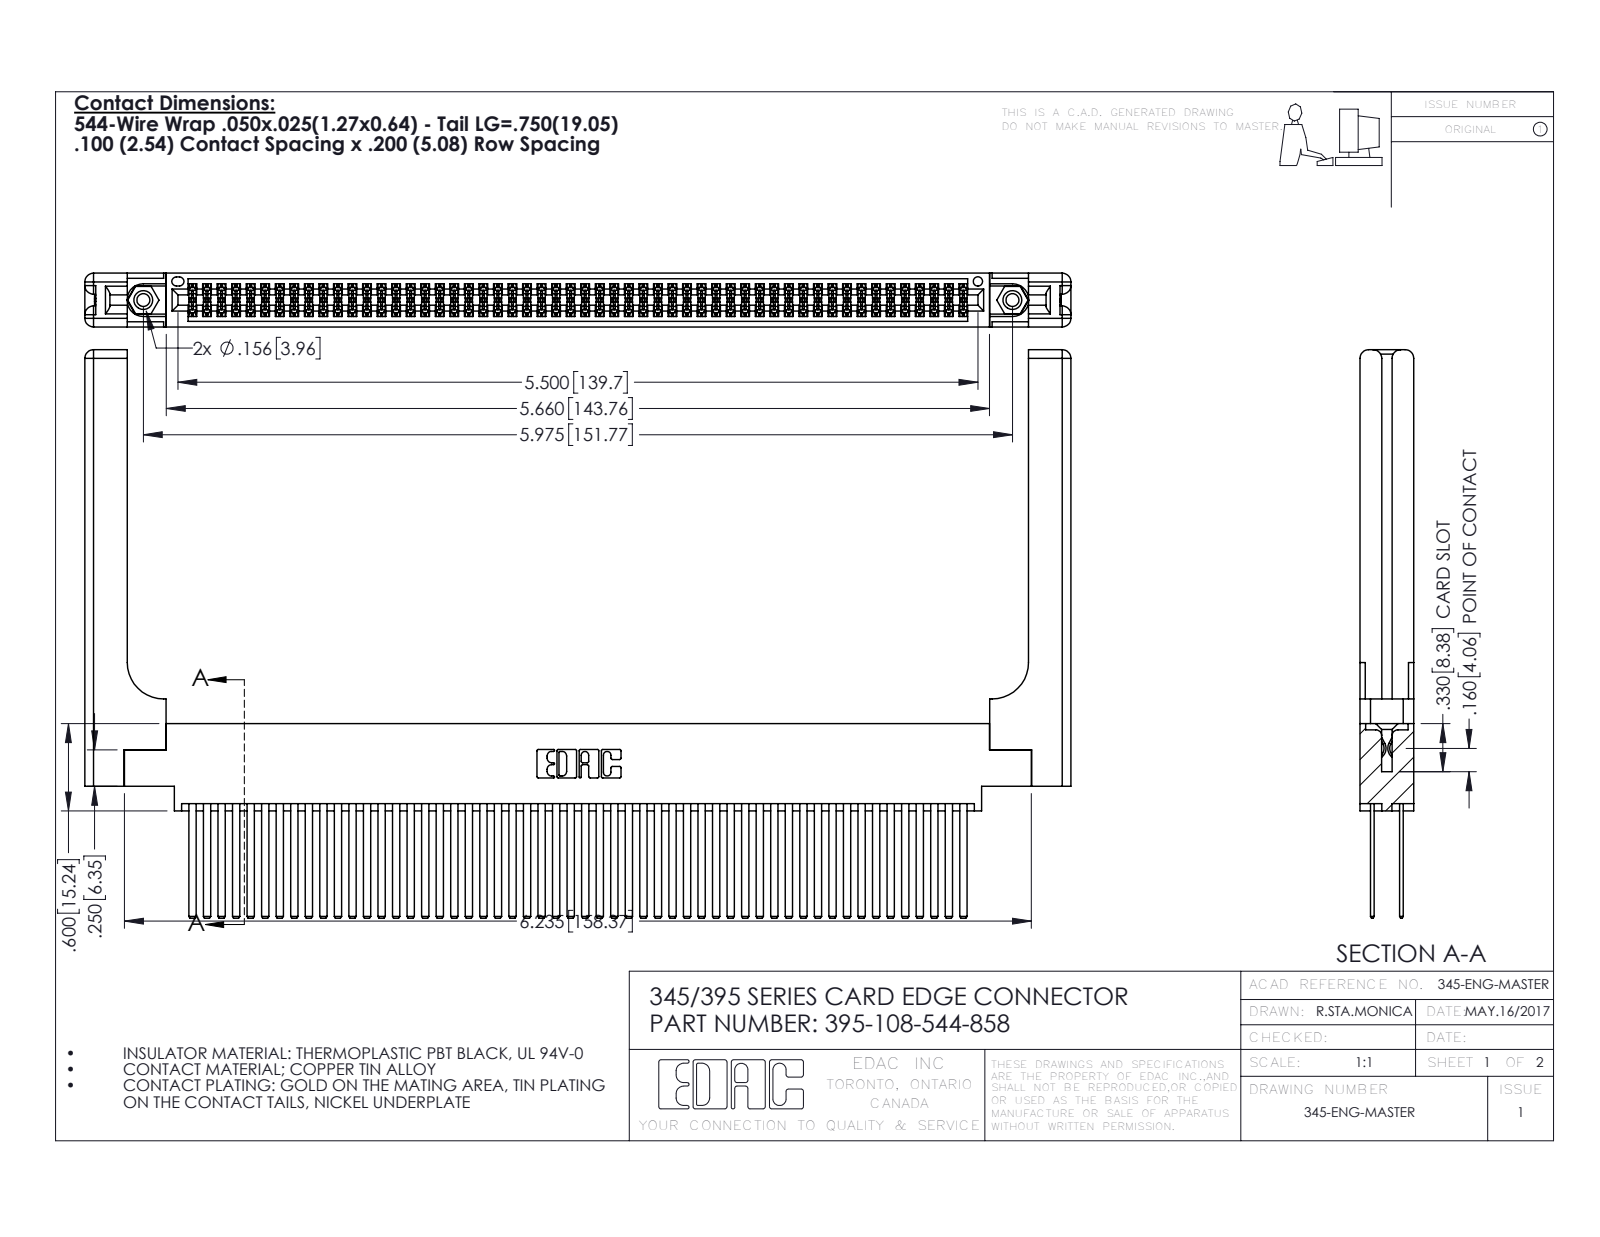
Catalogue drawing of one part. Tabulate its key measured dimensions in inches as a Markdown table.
| quantity | value |
| --- | --- |
| part name | 345 Part_0.170 Offset - 0.156 Dia-TH; 345-292-001_345-293-144; 395-108-544-858; 345-220-058_345-220-058 (+1 more) |
| STEP written by | SolidWorks 2016 (CONFIG_CONTROL_DESIGN) |
| units | inches |
| bodies | 113 solids, 5138 faces (3364 planar, 1714 cylindrical, 60 other) |
| overall size | 6.779 × 3.907 × 0.37 |
| volume | 1.63 in³ |
| surface area | 57.09 in² |
| round holes (diameter × count) | 0.089 × 2, 0.125 × 2, 0.156 × 2, 0.064 × 1 |
| round bosses / shafts (diameter × count) | 0.155 × 2 |
| partial cylindrical surfaces (radius × count) | 0.006 × 162, 0.01 × 22, 0.06 × 16, 0.007 × 6, 0.031 × 6, 0.026 × 3, 0.014 × 2, 0.019 × 2 |
| main face-to-face distances | 0.072, 0.298, 0.098, 0.272, 0.025, 0.2, 0.37, 0.225, 0.175, 0.148 |
| hole center spacings | 0.27, 5.739, 5.975 |
